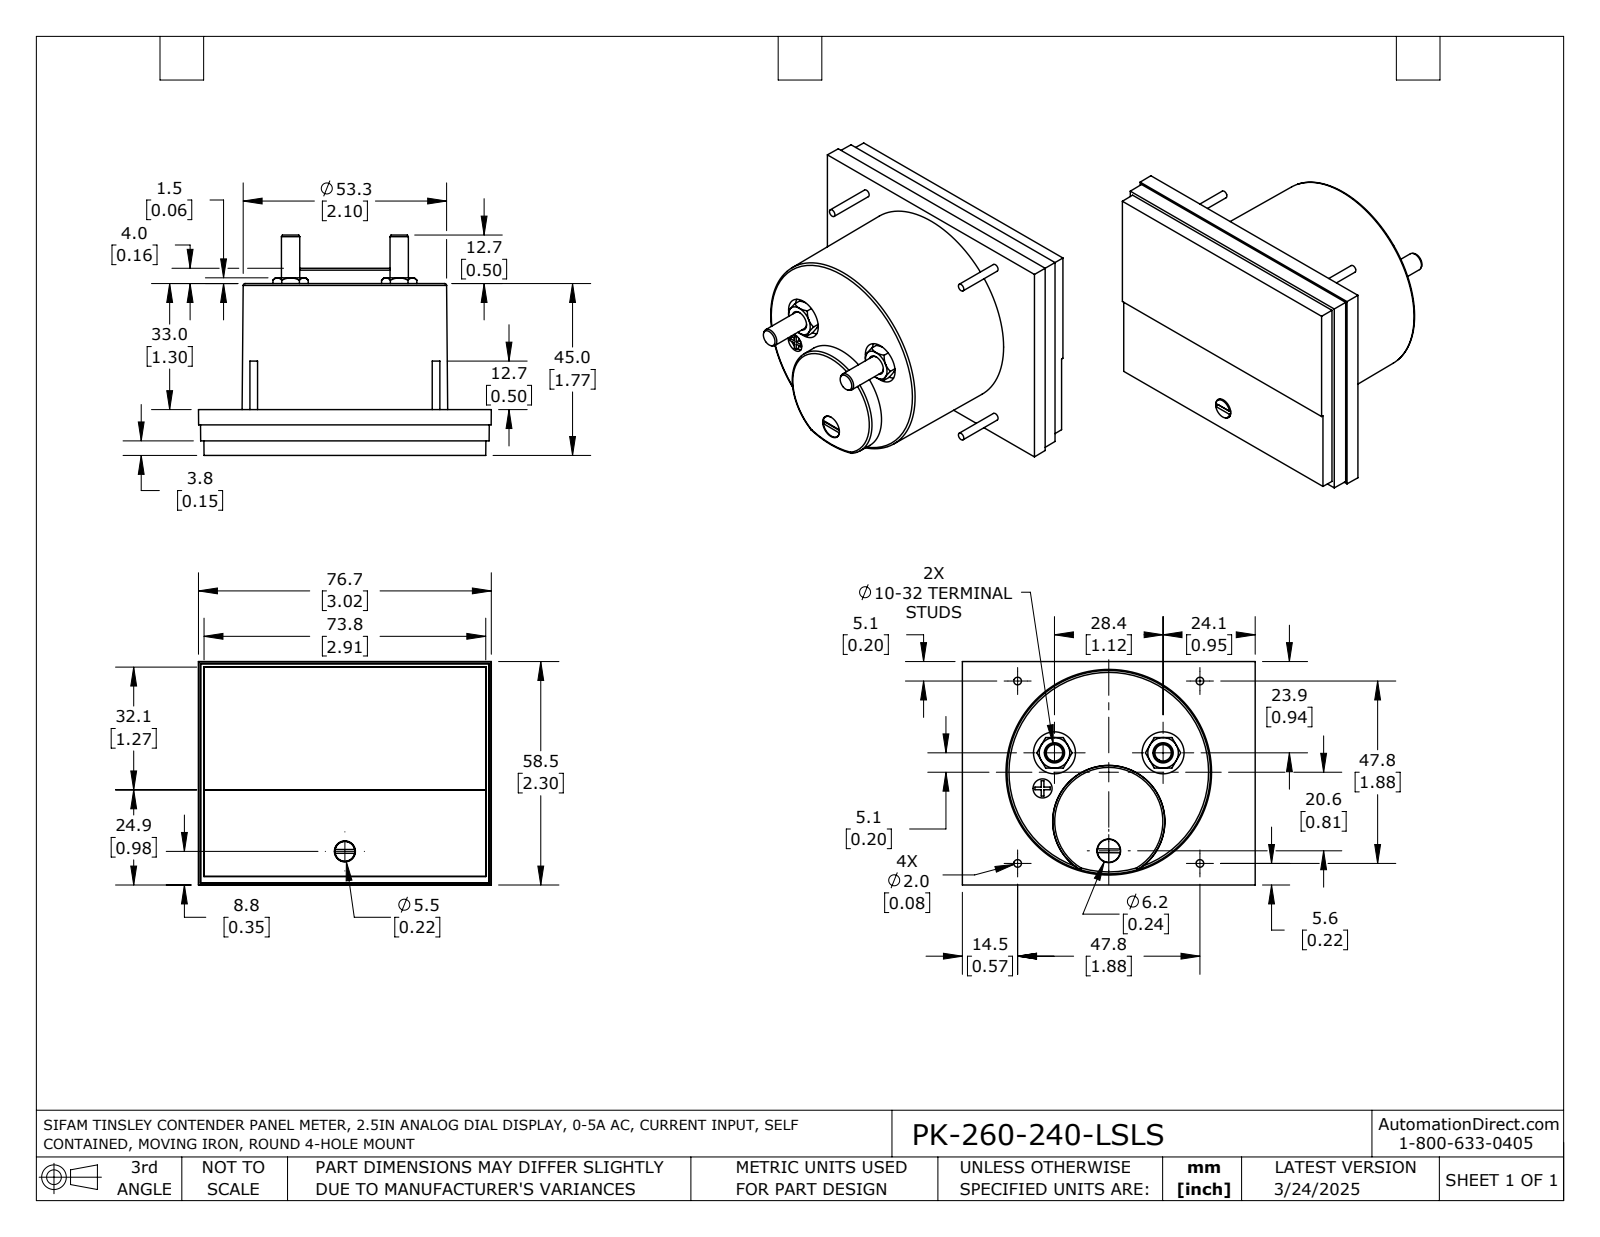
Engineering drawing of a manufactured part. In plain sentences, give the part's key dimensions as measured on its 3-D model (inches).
The part is named "PK-260-240-LSLS". Its 3-D file was written by "SolidWorks 2021 (AUTOMOTIVE_DESIGN)". It is 1 solid with 192 faces: 95 planar, 37 cylindrical and 60 other. Overall it measures 3.02 by 2.303 by 2.272 inches. Its volume is 7.657 cubic inches and its surface area 36.55 square inches. Round holes: 3 of diameter 0.197, 2 of diameter 0.433, 1 of diameter 0.209, 1 of diameter 0.217, 1 of diameter 0.244. Round bosses or shafts: 4 of diameter 0.079, 2 of diameter 0.189, 1 of diameter 0.236, 1 of diameter 0.205. Partial cylindrical surfaces (rounded edges, fillets, slot ends): 1 of radius 0.033. The main face-to-face distances are 0.02, 0.472, 0.13, 0.322, 0.15, 0.453, 0.057, 0.077, 0.396, 0.073. The hole center spacings are 1.155, 1.16, 0.387, 0.938, 0.942, 1.12, 1.295.
